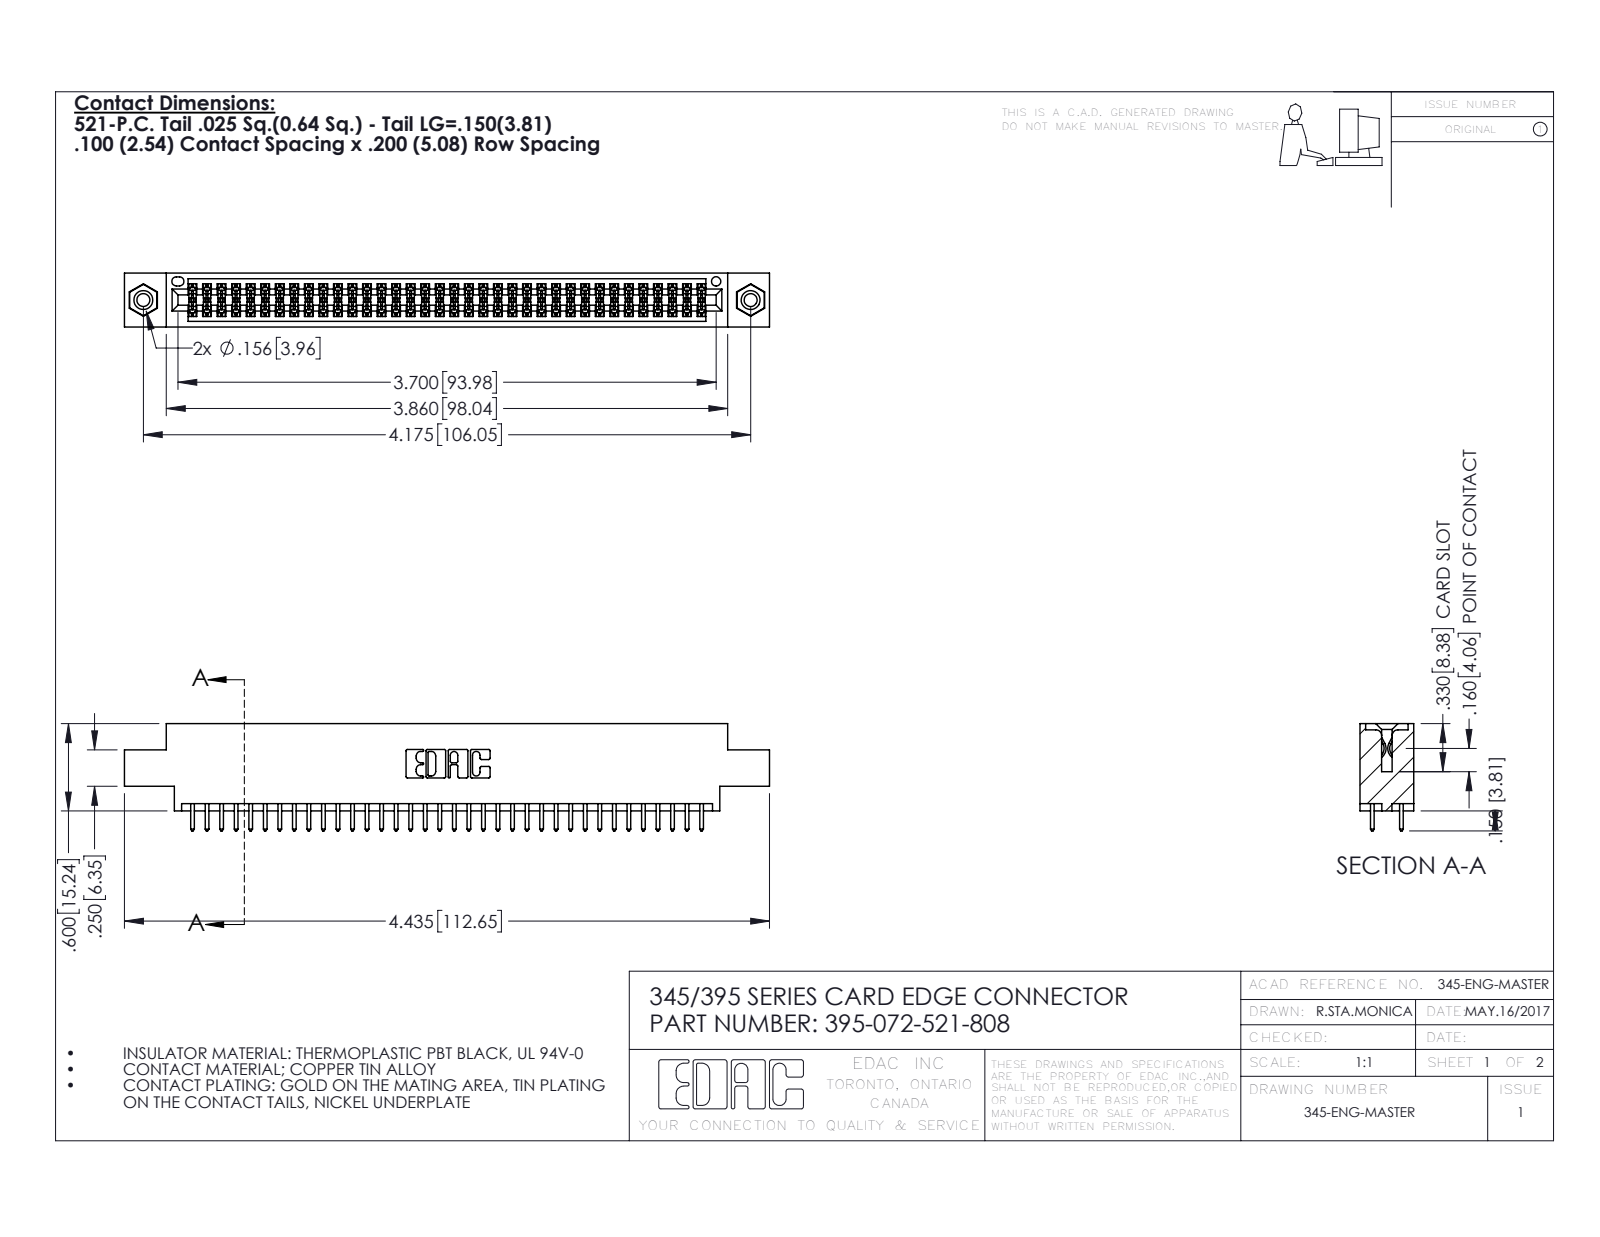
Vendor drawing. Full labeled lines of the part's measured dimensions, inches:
Part name (STEP PRODUCT): 345-250-001_345-250-003-102; 345-292-001_345-293-121; 345 Part_0.170 Offset - 0.156 Dia-TI; 395-072-521-808
STEP written by: SolidWorks 2016 (CONFIG_CONTROL_DESIGN)
Units: inches
Bodies: 75 solids, 3790 faces (2492 planar, 1282 cylindrical, 16 other)
Overall size (bounding box): 4.435 × 0.737 × 0.37
Volume: 0.655 in³ · Surface area: 24.37 in²
Round holes (diameter × count): ⌀0.089 ×2, ⌀0.125 ×2, ⌀0.156 ×2, ⌀0.064 ×1
Round bosses / shafts (diameter × count): ⌀0.155 ×2
Partial cylindrical surfaces — rounded edges, fillets, slot ends (radius × count): R0.006 ×108, R0.01 ×72, R0.01 ×22, R0.007 ×6, R0.031 ×6, R0.026 ×3, R0.014 ×2, R0.019 ×2
Main face-to-face distances: 0.072, 0.298, 0.37, 0.2, 0.098, 0.272, 0.025, 0.225, 0.175, 0.149
Hole centre spacings: 0.27, 3.939, 4.175
